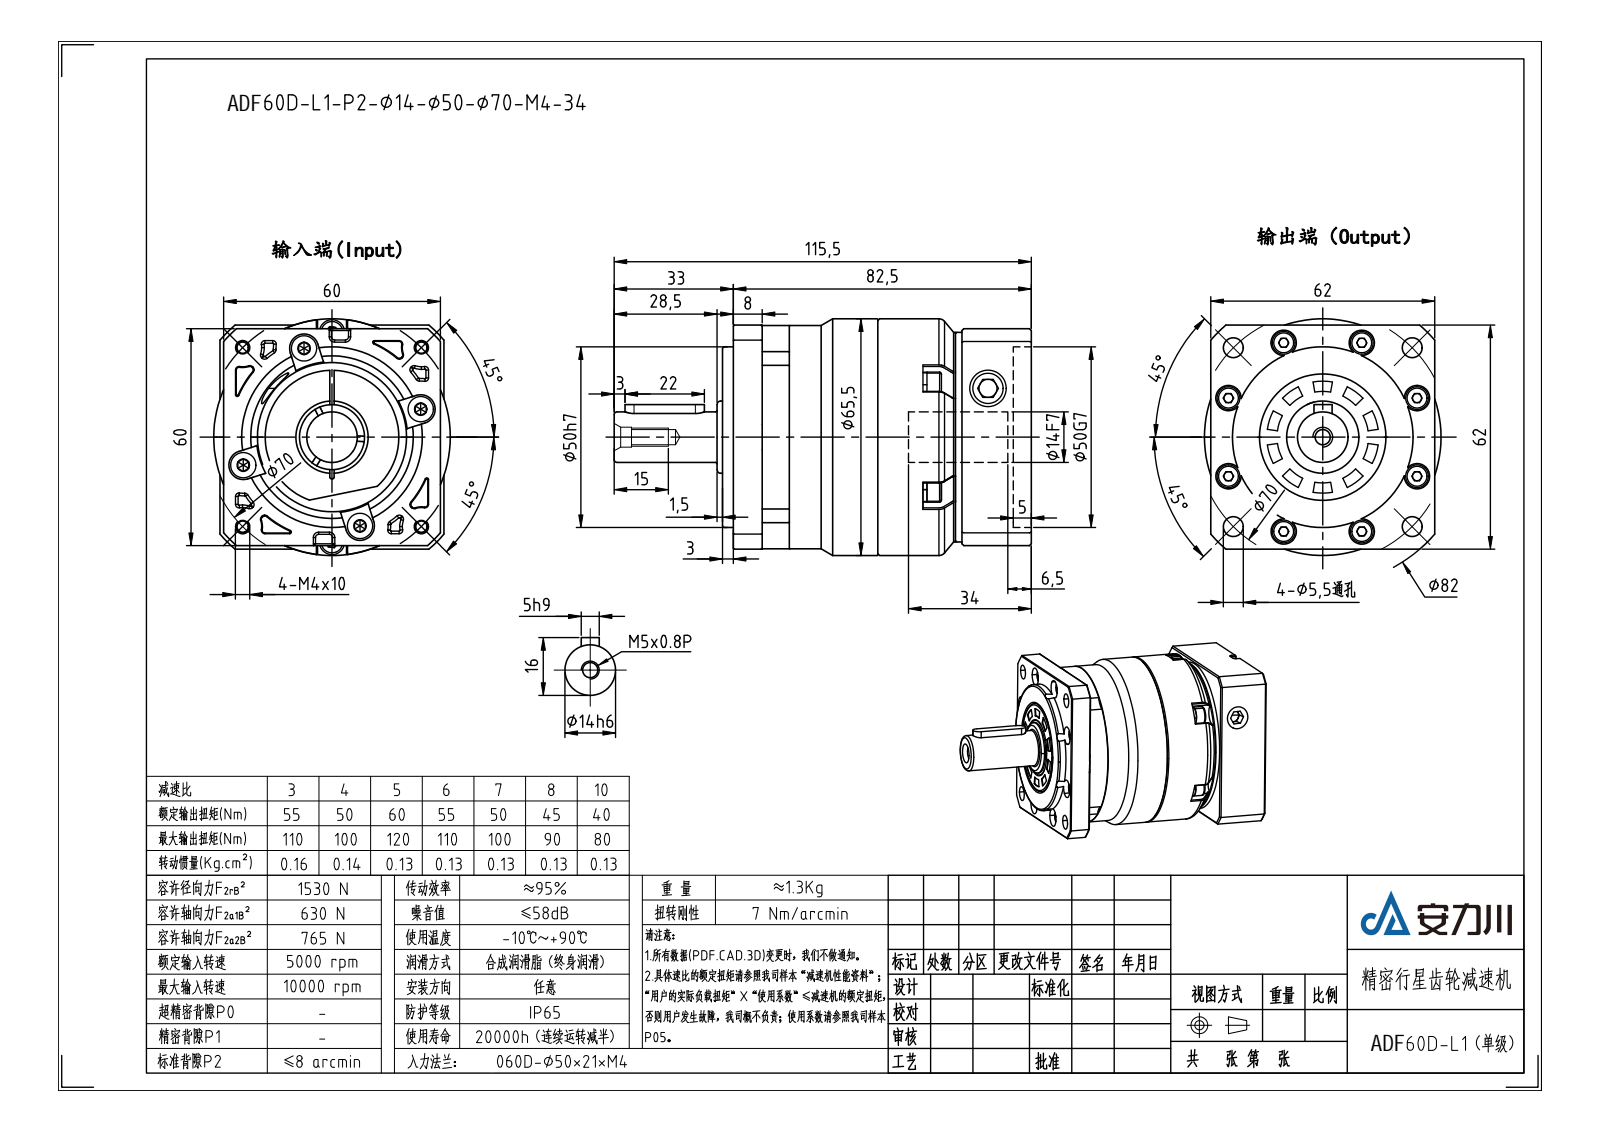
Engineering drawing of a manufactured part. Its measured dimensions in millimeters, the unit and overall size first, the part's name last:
Units: millimetres
Overall size (bounding box): 115.5 × 65.5 × 65.5
Round holes (diameter × count): ⌀3.3 ×16, ⌀4.5 ×10, ⌀5.5 ×6, ⌀4.2 ×1, ⌀4.3 ×1, ⌀8.5 ×1, ⌀9 ×1, ⌀14 ×1, ⌀14.5 ×1, ⌀31.86 ×1, ⌀35 ×1, ⌀38 ×1
Round bosses / shafts (diameter × count): ⌀65.5 ×1, ⌀61.8 ×1, ⌀58 ×1, ⌀51.5 ×1, ⌀50 ×1, ⌀43 ×1, ⌀42 ×1, ⌀37 ×1
Partial cylindrical surfaces — rounded edges, fillets, slot ends (radius × count): R0.3 ×56, R0.5 ×12, R4 ×10, R1 ×8, R5 ×4, R37.5 ×3, R0.4 ×2, R2.5 ×2
Main face-to-face distances: 21.5, 24.5, 18.5, 3, 43, 46, 1, 15.5, 67, 60
Hole centre spacings: 29, 14.01, 21.62, 28.25, 35.59, 39.95, 52.2, 52.73
Volume: 246 509 mm³ · Surface area: 71 336 mm²
Bodies: 11 solids, 970 faces (236 planar, 312 cylindrical, 422 other)
Part name (STEP PRODUCT): hex socket set screws with cone point gb_GB_FASTENER_SCREWS_HSCP M10X8-N; 11-输入法兰FAB060D-50-70-M4.; 3-输入端壳体FAD064D; FAB060D输出行星架-14轴 (+7 more)
STEP written by: SolidWorks 2014 (AUTOMOTIVE_DESIGN)
